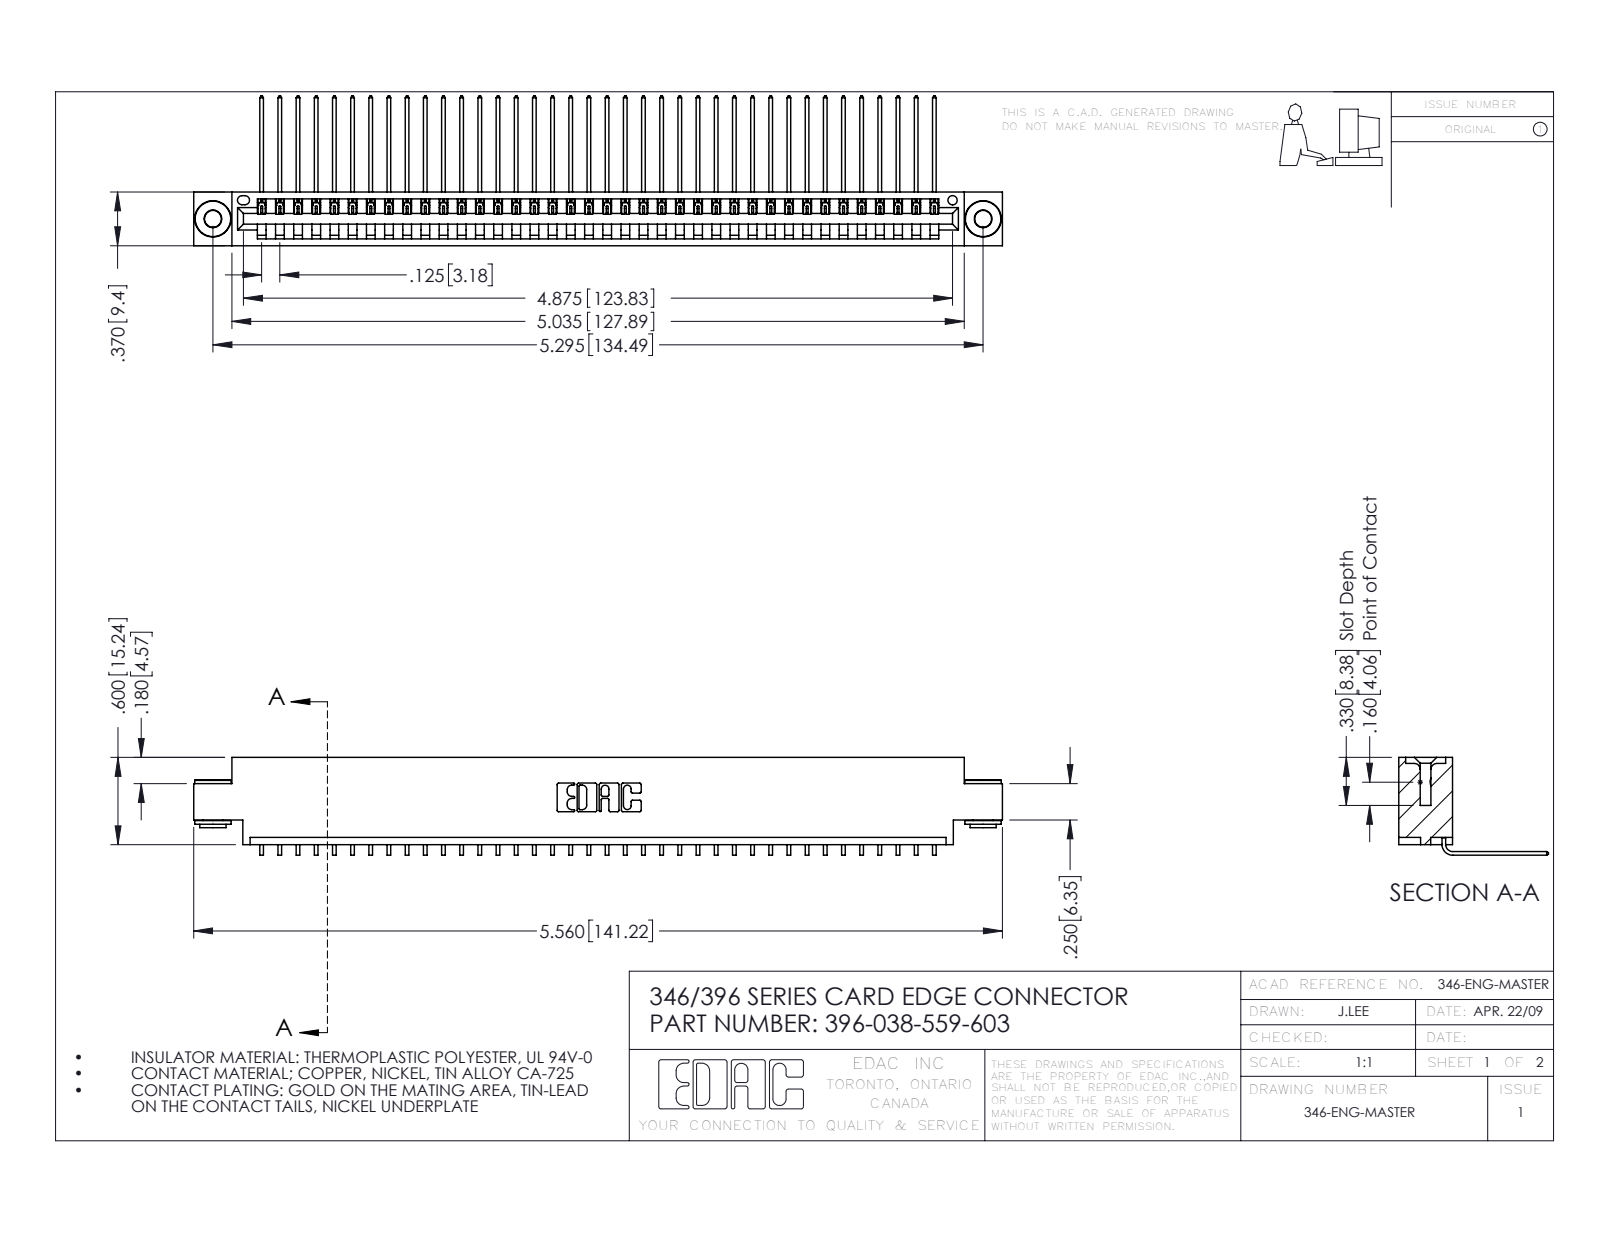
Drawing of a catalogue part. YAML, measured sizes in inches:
part_name: "345-250-002_345-250-002-102; 396-038-559-603; 345-292-001_558 559 Tail - 1; 346 Part_0.170 Offset - 0.156 Dia-TH"
step_written_by: "SolidWorks 2016 (CONFIG_CONTROL_DESIGN)"
units: inches
bodies: {solids: 41, faces: 2444, planar: 1686, cylindrical: 750, other: 8}
overall_size: [5.56, 1.03, 0.673]
volume: 0.823
surface_area: 27.81
round_holes:
  - {diameter: 0.116, count: 2}
  - {diameter: 0.156, count: 2}
  - {diameter: 0.064, count: 1}
round_bosses_or_shafts:
  - {diameter: 0.25, count: 2}
  - {diameter: 0.18, count: 2}
  - {diameter: 0.136, count: 2}
partial_cylinders:
  - {radius: 0.006, count: 76}
  - {radius: 0.01, count: 22}
  - {radius: 0.007, count: 6}
  - {radius: 0.031, count: 6}
  - {radius: 0.026, count: 3}
  - {radius: 0.031, count: 2}
  - {radius: 0.04, count: 2}
  - {radius: 0.014, count: 1}
face_to_face_distances: [0.048, 0.322, 0.37, 0.025, 0.25, 0.072, 0.298, 0.148, 0.222, 0.1]
hole_center_spacings: [0.246, 5.086, 5.295]
